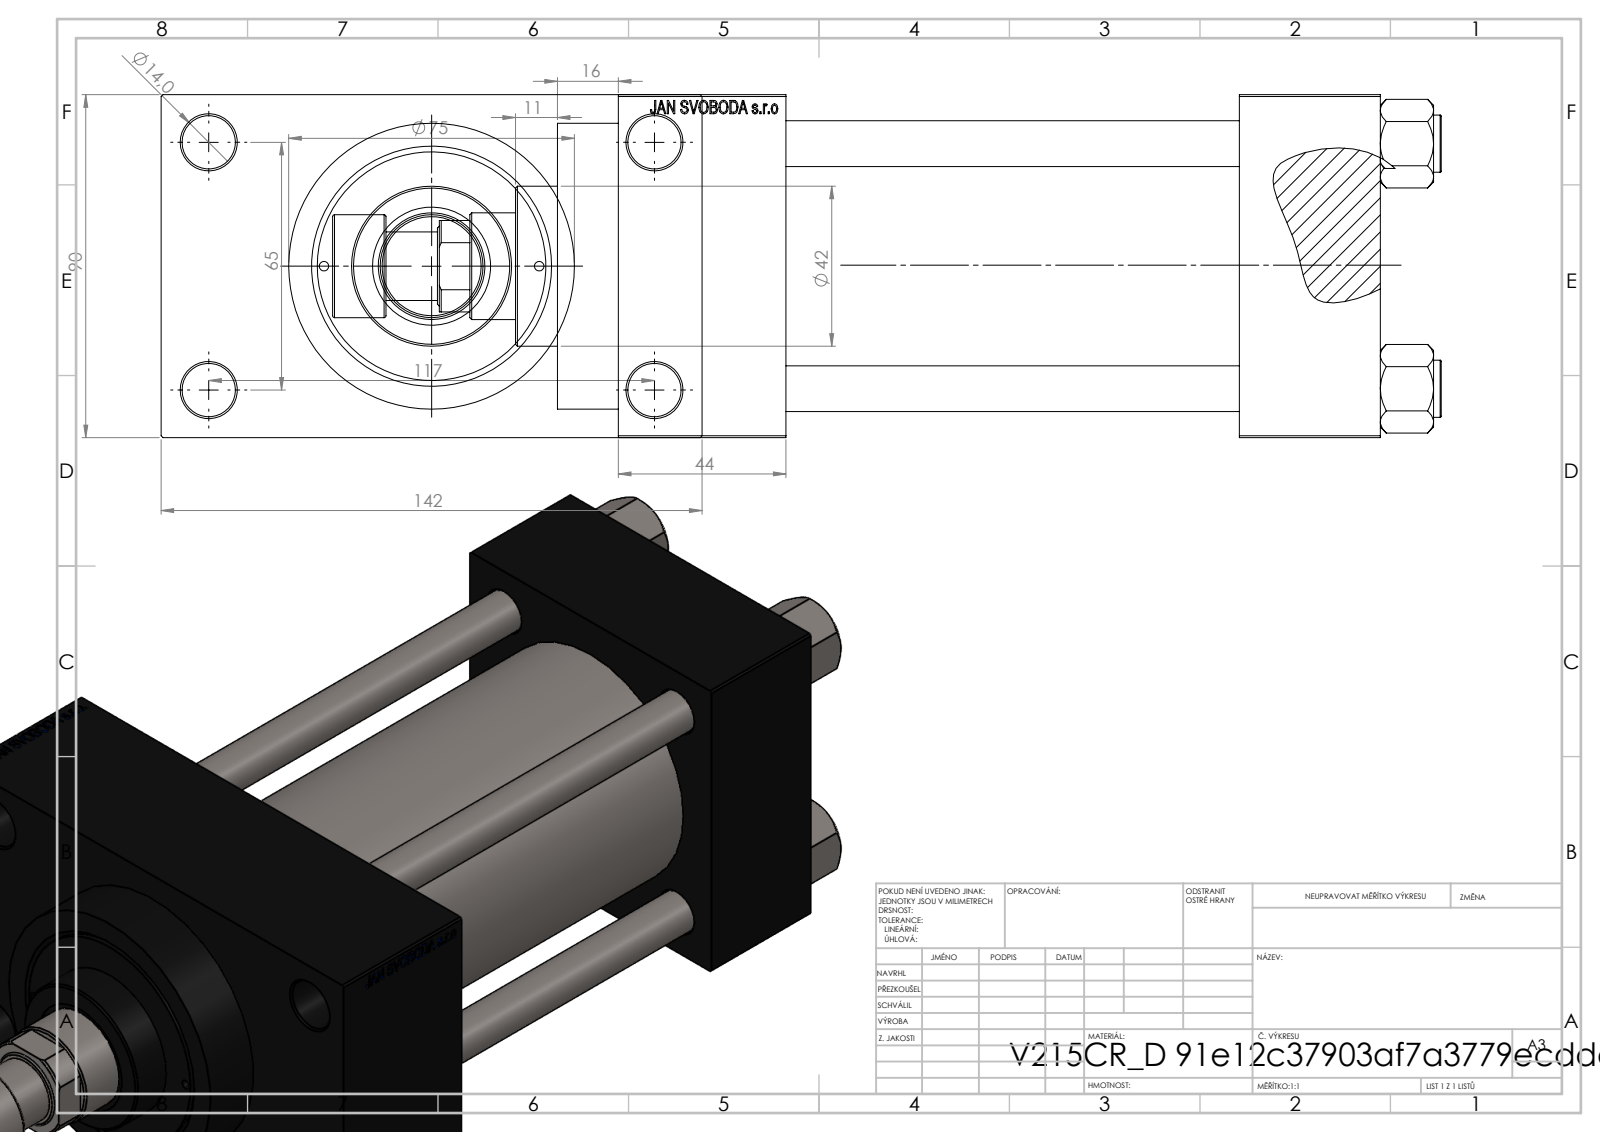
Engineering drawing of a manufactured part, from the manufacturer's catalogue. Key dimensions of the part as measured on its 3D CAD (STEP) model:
Part name (STEP PRODUCT): V215CR_D_TYCINKA; V215CR_D_Body; V215CR_VCP_D; V215_VC_A (+2 more)
STEP written by: SolidWorks 2019 (CONFIG_CONTROL_DESIGN)
Units: millimetres
Bodies: 12 solids, 1125 faces (503 planar, 96 cylindrical, 526 other)
Overall size (bounding box): 291 × 142 × 90
Volume: 1 209 000 mm³ · Surface area: 242 693 mm²
Round holes (diameter × count): ⌀12 ×4, ⌀14 ×4, ⌀2.5 ×2, ⌀7 ×2, ⌀20.96 ×2, ⌀30 ×2, ⌀18.5 ×1, ⌀28 ×1, ⌀31 ×1, ⌀50 ×1, ⌀60 ×1, ⌀63 ×1
Round bosses / shafts (diameter × count): ⌀15 ×4, ⌀75 ×1, ⌀69 ×1, ⌀42 ×1, ⌀27 ×1, ⌀18 ×1
Main face-to-face distances: 90, 119, 37, 156, 163, 200, 44, 26, 116, 16
Hole centre spacings: 26.35, 32.39, 44.4, 45.47, 64.3, 66.92, 68.42, 69.81
